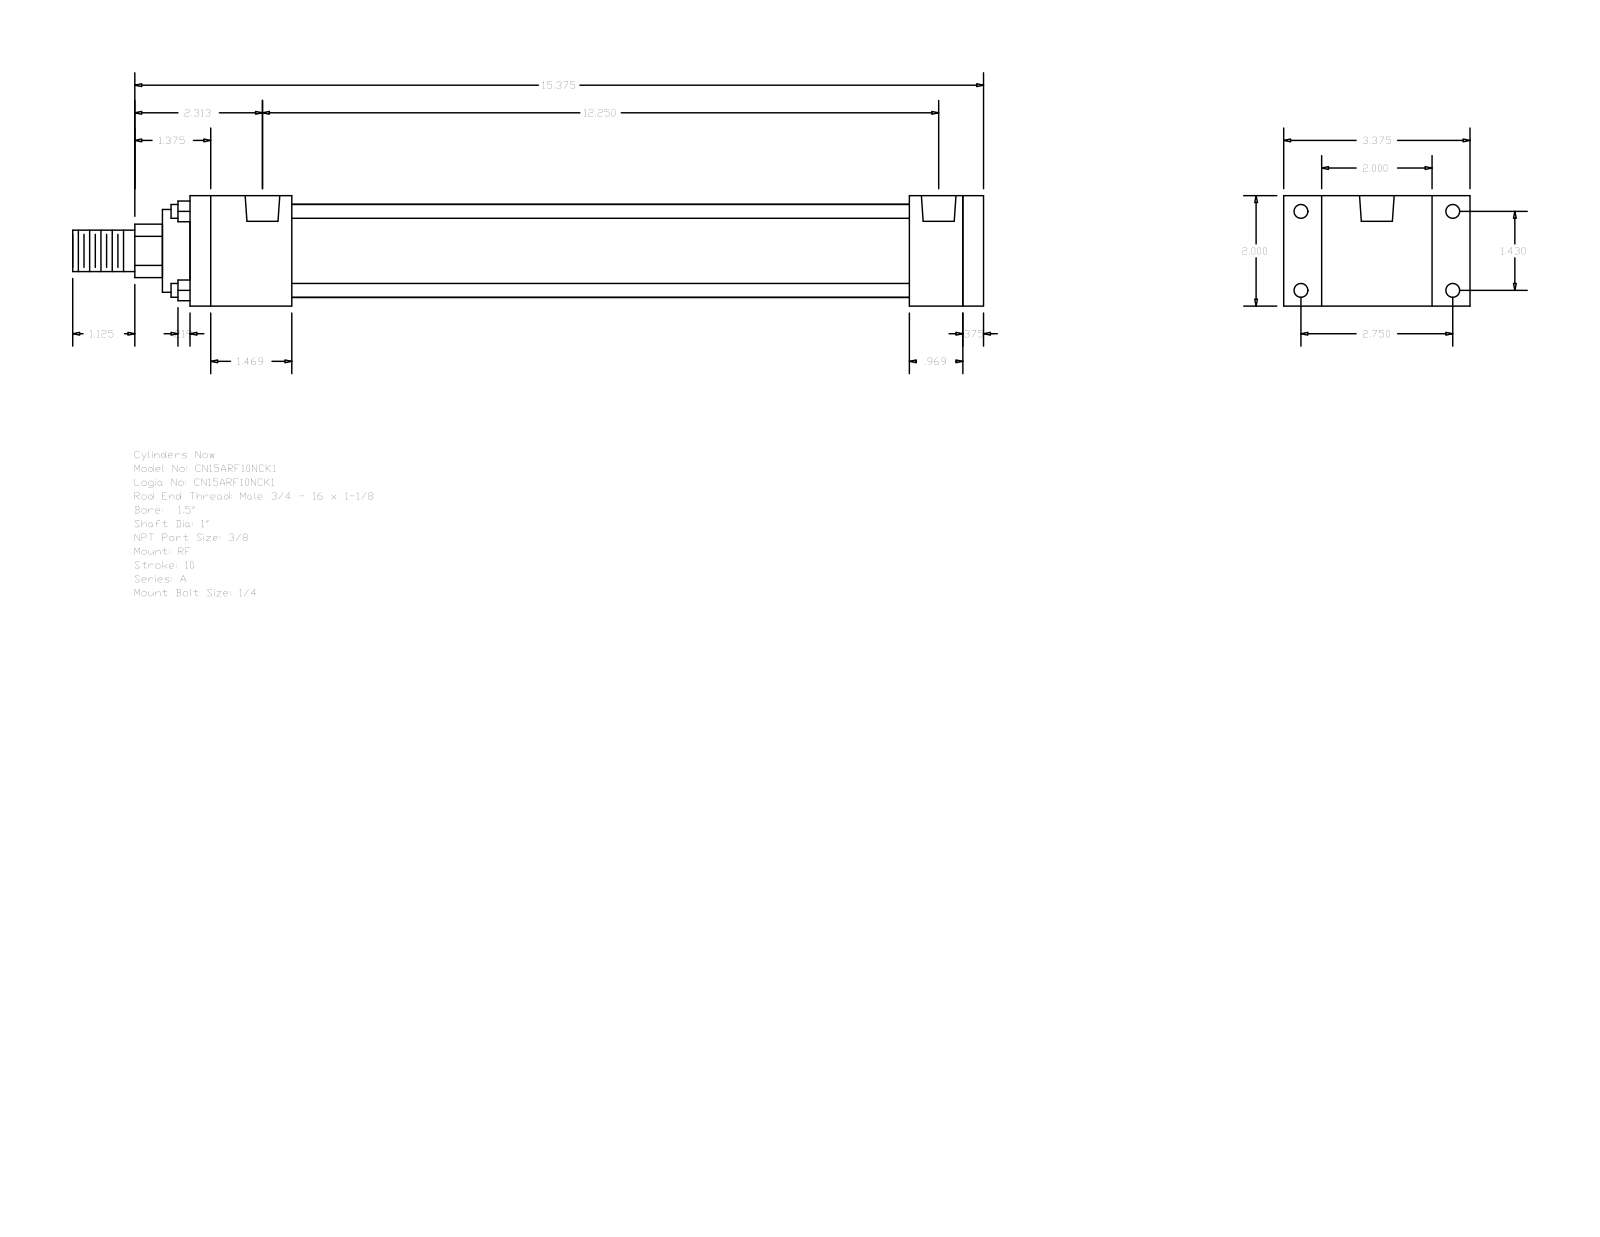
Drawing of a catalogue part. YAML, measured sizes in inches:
part_name: "A_RF__0150_1"
step_written_by: "GSSL Pune (CONFIG_CONTROL_DESIGN)"
units: inches
bodies: {solids: 0, faces: 92, planar: 64, cylindrical: 28, other: 0}
overall_size: [16.5, 3.375, 2]
round_holes:
  - {diameter: 0.219, count: 4}
  - {diameter: 0.25, count: 4}
  - {diameter: 0.627, count: 2}
round_bosses_or_shafts:
  - {diameter: 0.25, count: 4}
  - {diameter: 1.69, count: 1}
  - {diameter: 1.5, count: 1}
  - {diameter: 1, count: 1}
  - {diameter: 0.75, count: 1}
partial_cylinders:
  - {radius: 0.484, count: 1}
face_to_face_distances: [2, 0.375, 14, 14.375, 13.031, 0.969, 1.344, 1.844, 11.187, 12.156]
hole_center_spacings: [0.156, 1.43, 2.75, 3.099, 11.937, 12.094, 12.25]
